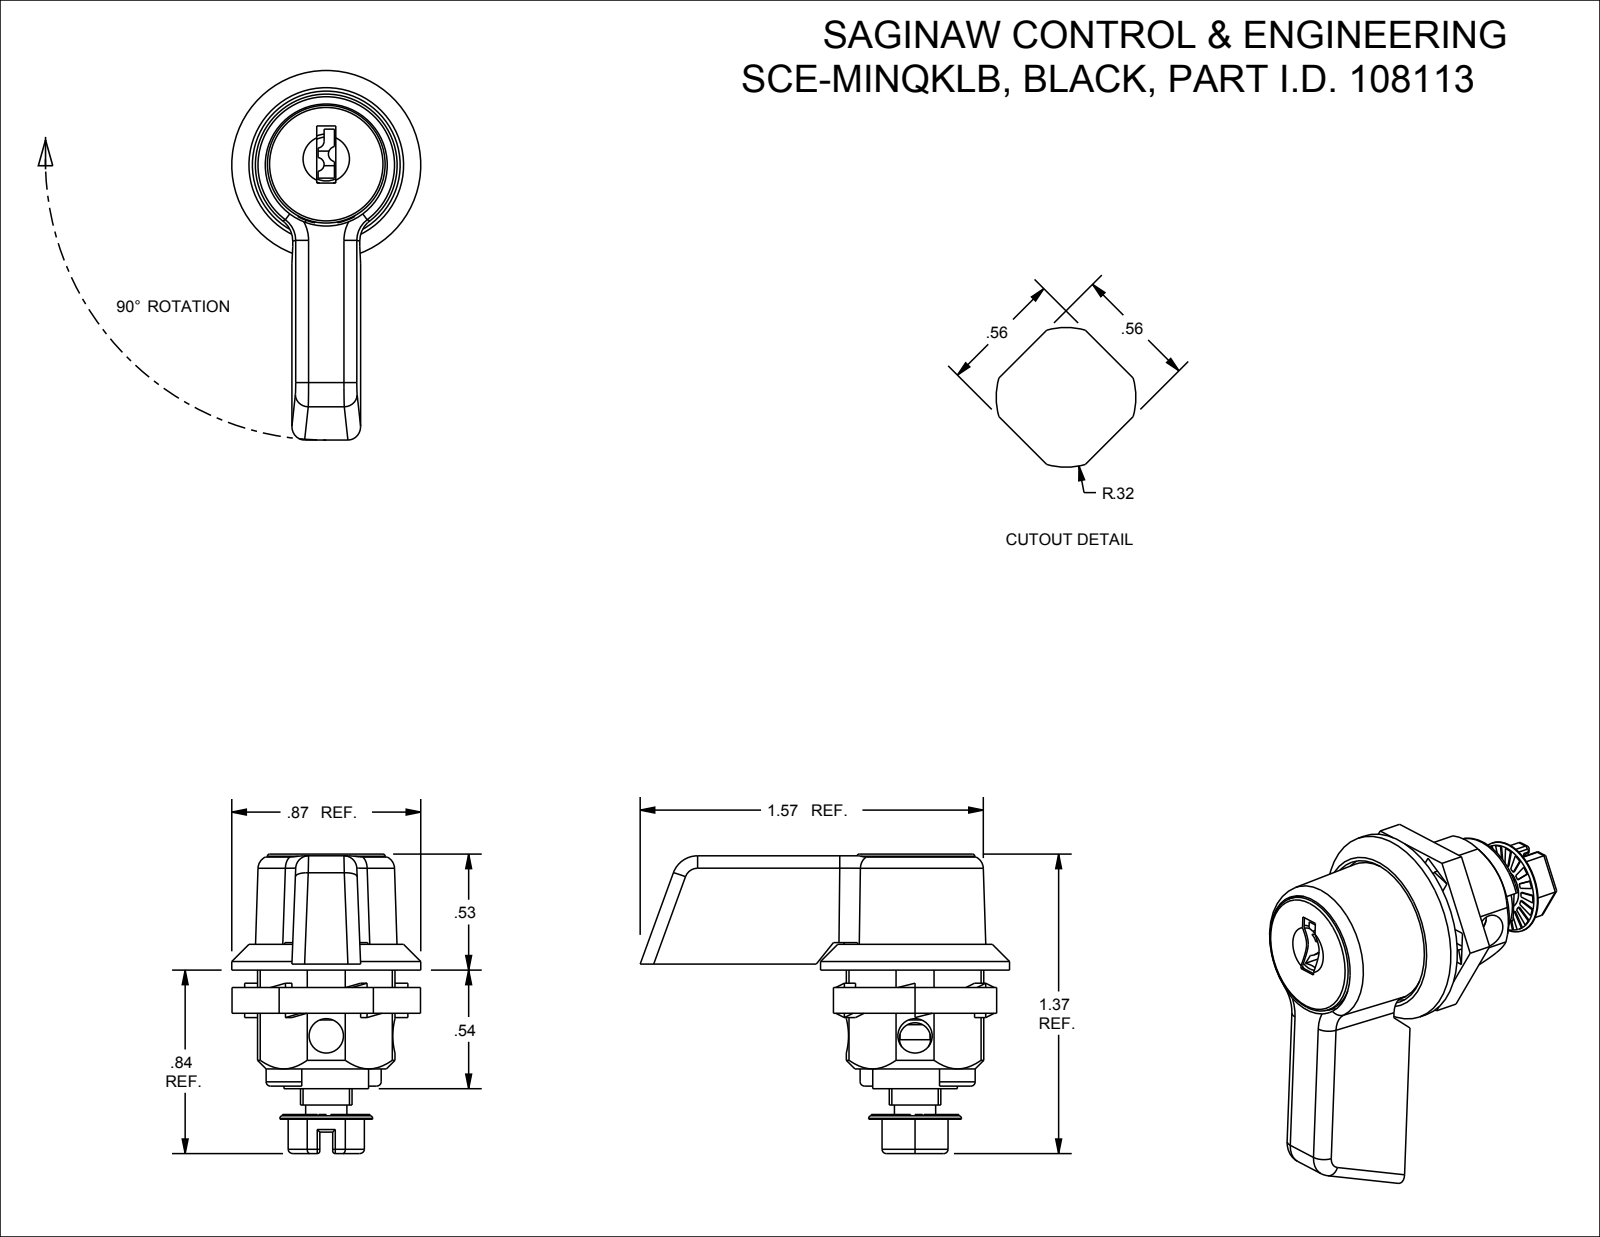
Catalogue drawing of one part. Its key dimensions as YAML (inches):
part_name: "SEC-MINQKLB"
step_written_by: "SolidWorks 2021 (AUTOMOTIVE_DESIGN)"
units: inches
bodies: {solids: 7, faces: 559, planar: 360, cylindrical: 152, other: 47}
overall_size: [1.72, 1.372, 0.92]
volume: 0.41
surface_area: 12.74
round_holes:
  - {diameter: 0.157, count: 3}
  - {diameter: 0.071, count: 1}
  - {diameter: 0.144, count: 1}
  - {diameter: 0.224, count: 1}
  - {diameter: 0.236, count: 1}
  - {diameter: 0.398, count: 1}
  - {diameter: 0.404, count: 1}
  - {diameter: 0.498, count: 1}
  - {diameter: 0.52, count: 1}
  - {diameter: 0.559, count: 1}
  - {diameter: 0.677, count: 1}
round_bosses_or_shafts:
  - {diameter: 0.866, count: 1}
  - {diameter: 0.551, count: 1}
  - {diameter: 0.539, count: 1}
  - {diameter: 0.516, count: 1}
  - {diameter: 0.492, count: 1}
  - {diameter: 0.425, count: 1}
  - {diameter: 0.394, count: 1}
  - {diameter: 0.388, count: 1}
partial_cylinders:
  - {radius: 0.012, count: 30}
  - {radius: 0.02, count: 10}
  - {radius: 0.039, count: 8}
  - {radius: 0.059, count: 4}
  - {radius: 0.118, count: 3}
  - {radius: 0.031, count: 2}
  - {radius: 0.035, count: 1}
  - {radius: 0.171, count: 1}
face_to_face_distances: [0.522, 0.551, 0.059, 0.748, 0.531, 0.463, 0.197, 0.118, 0.08, 0.193]
hole_center_spacings: [0.126]
